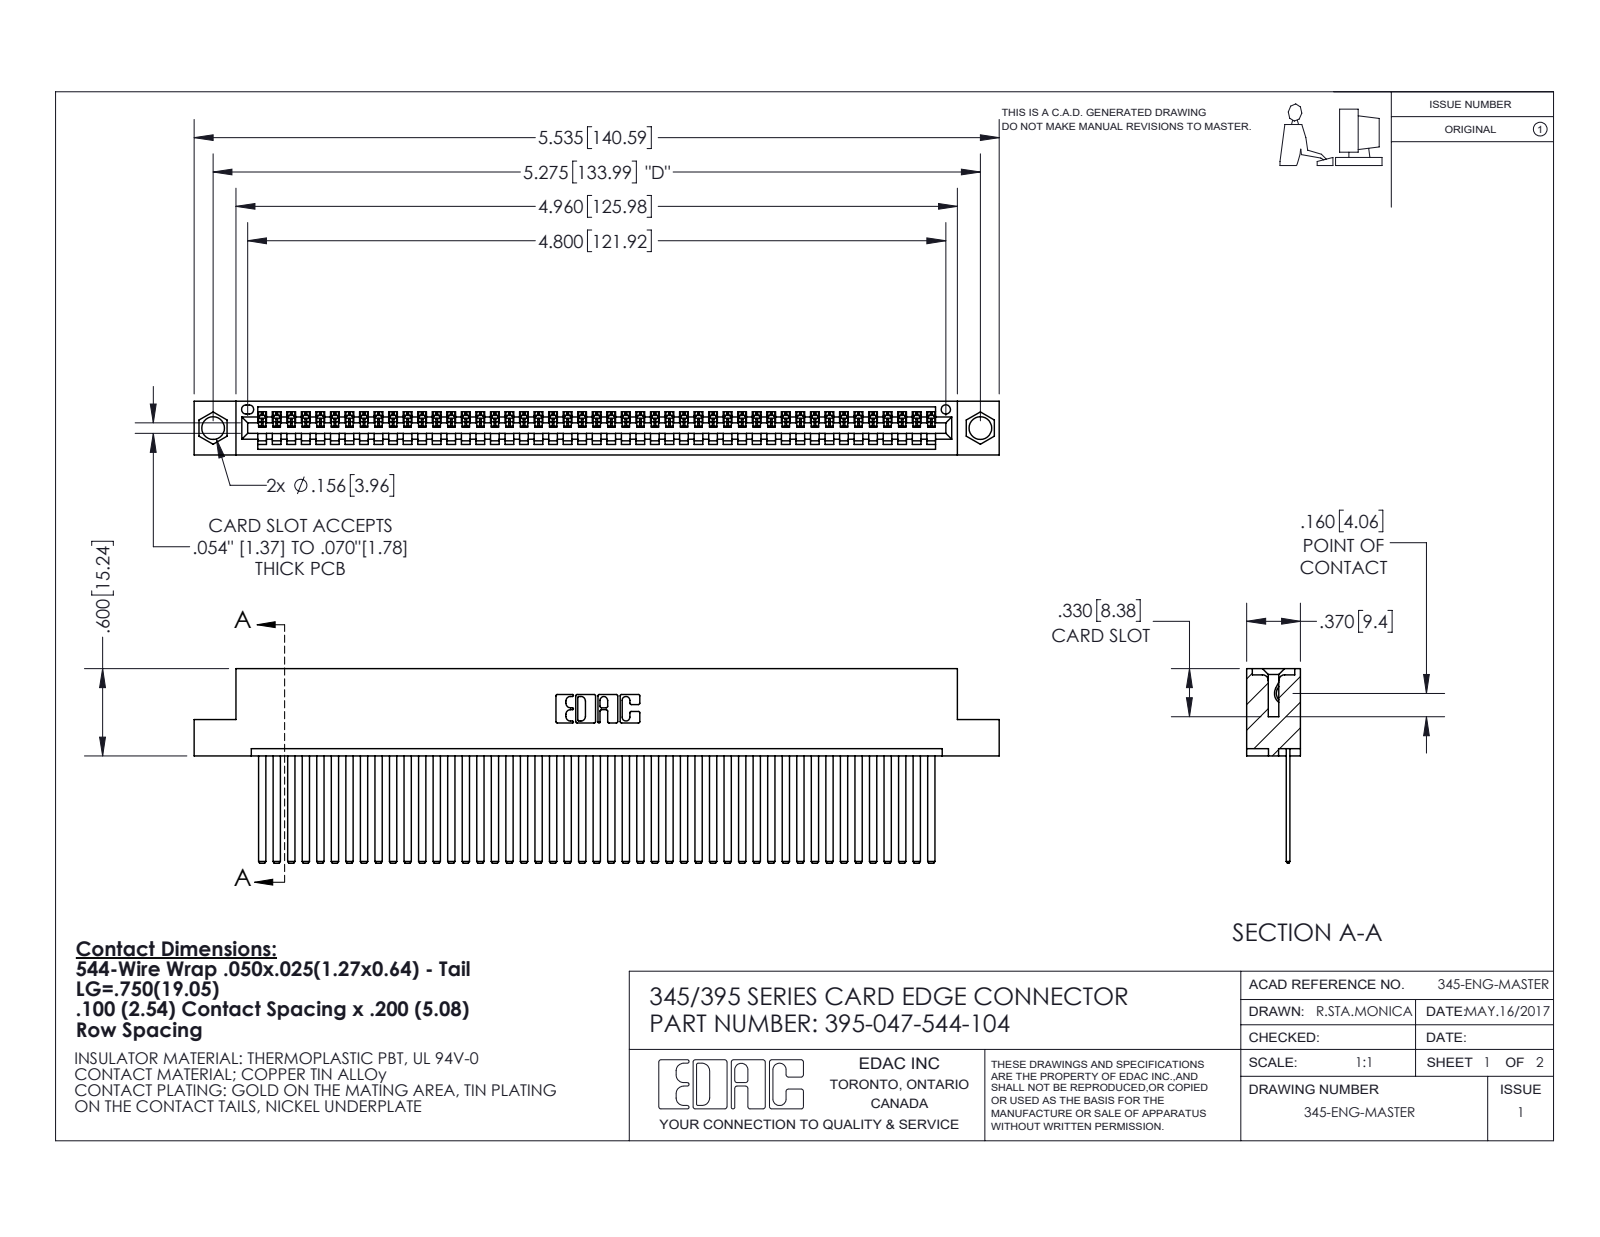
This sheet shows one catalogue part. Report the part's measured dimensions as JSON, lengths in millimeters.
{"part_name": "345-292-001_345-293-144; 395-047-544-104; 345 Part_Flush Mounting Lugs - 0.156 Dia-TI", "step_written_by": "SolidWorks 2020 (CONFIG_CONTROL_DESIGN)", "units": "millimeters", "bodies": {"solids": 48, "faces": 2584, "planar": 1786, "cylindrical": 798, "other": 0}, "overall_size": [140.6, 34, 9.4], "volume_mm3": 13800, "surface_area_mm2": 19930, "round_holes": [[4, 2], [1.6, 1]], "partial_cylinders_radius": [[0.2, 94], [0.3, 22], [0.2, 6], [0.8, 6], [0.7, 3], [0.8, 2], [1, 2], [0.4, 1]], "face_to_face_distances": [1.8, 7.6, 0.6, 2.5, 6.9, 9.4, 5.1, 5.7, 3.8, 1.8], "hole_center_spacings": [6.9, 128, 134]}
